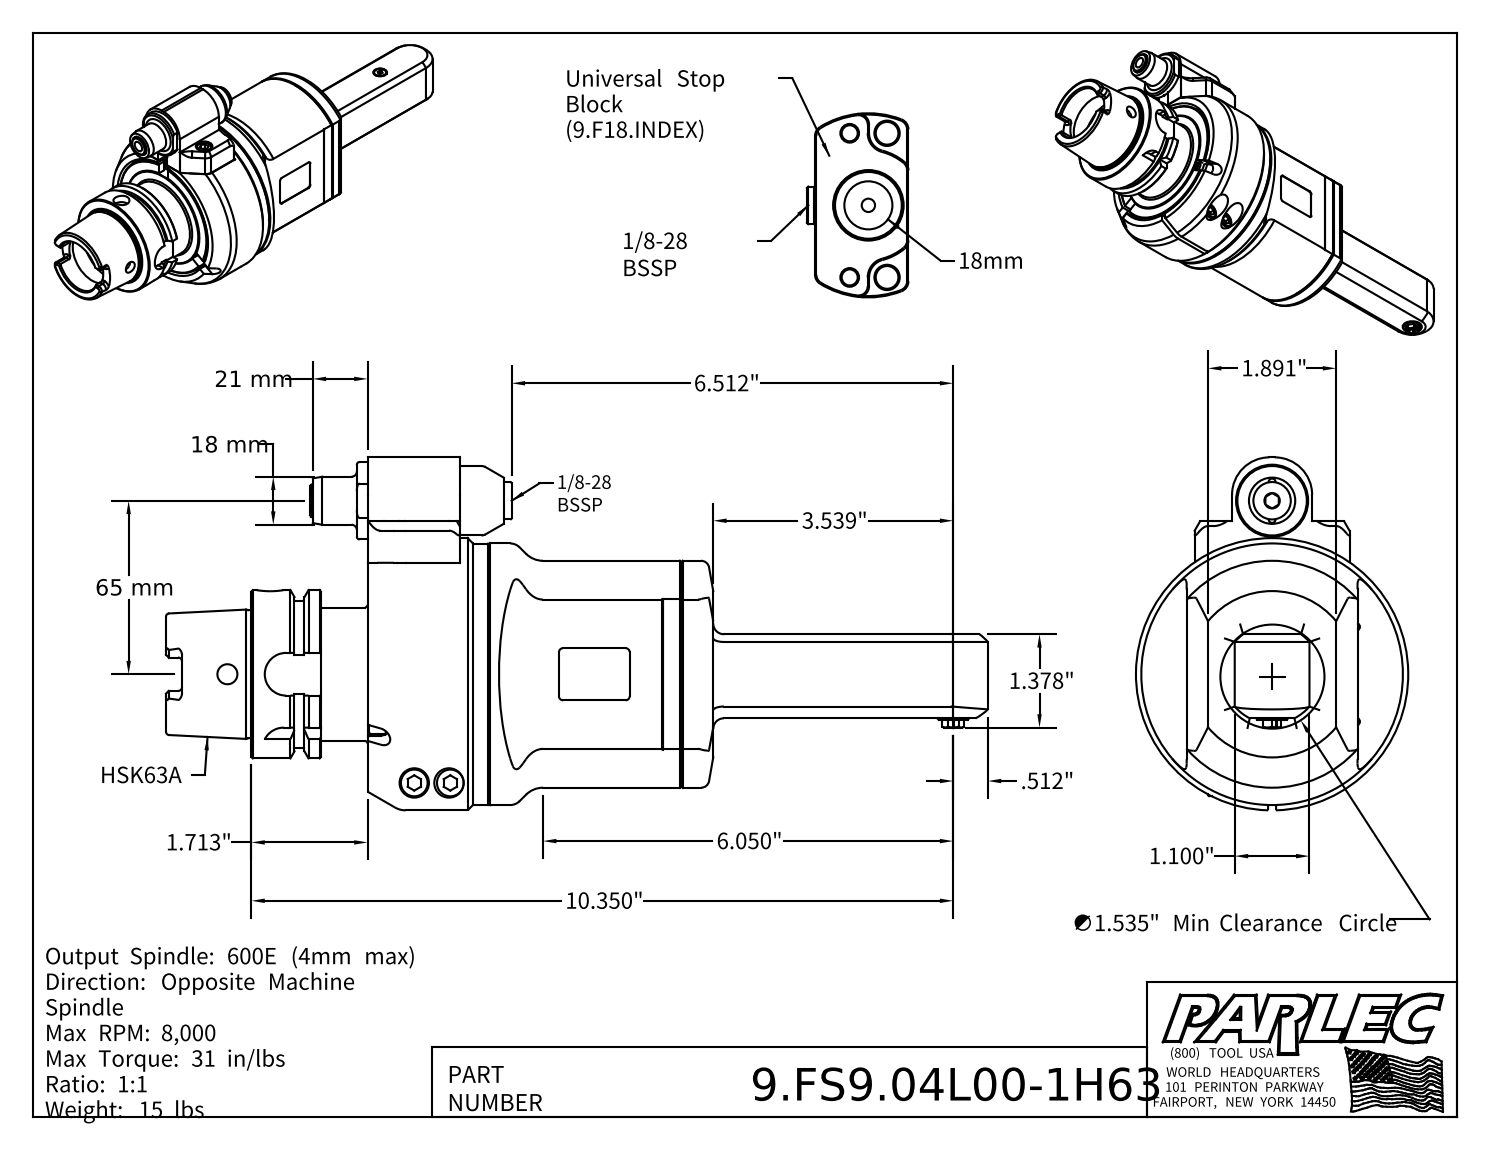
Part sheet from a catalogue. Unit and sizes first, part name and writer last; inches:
Units: inches
Overall size (bounding box): 12.122 × 5.206 × 4.016
Round holes (diameter × count): ⌀0.102 ×2, ⌀0.118 ×2, ⌀0.165 ×2, ⌀0.197 ×2, ⌀0.335 ×2, ⌀0.409 ×2, ⌀0.433 ×2, ⌀0.492 ×2, ⌀0.098 ×1, ⌀0.157 ×1, ⌀0.256 ×1, ⌀0.276 ×1
Round bosses / shafts (diameter × count): ⌀0.394 ×4, ⌀0.236 ×4, ⌀0.315 ×3, ⌀0.709 ×2, ⌀0.098 ×2, ⌀4.016 ×1, ⌀3.858 ×1, ⌀3.85 ×1
Partial cylindrical surfaces — rounded edges, fillets, slot ends (radius × count): R0.059 ×10, R0.157 ×10, R0.079 ×8, R0.113 ×4, R0.315 ×4, R0.551 ×3, R0.02 ×2, R0.039 ×2
Main face-to-face distances: 0.709, 0.118, 1.811, 1.102, 1.26, 1.378, 1.024, 0.157, 0.02, 2.52
Hole centre spacings: 0.276, 0.512, 0.551, 1.081, 1.72, 2.208, 2.283, 2.559
Volume: 62.01 in³ · Surface area: 233.1 in²
Bodies: 5 solids, 538 faces (267 planar, 139 cylindrical, 132 other)
Part name (STEP PRODUCT): 9.FS9.04L00-1H63; 9_GA1_566_2 (Type 1, H63A, 65mm); 9_FS9_04L00
STEP written by: Autodesk Inventor 2022 (AUTOMOTIVE_DESIGN)
